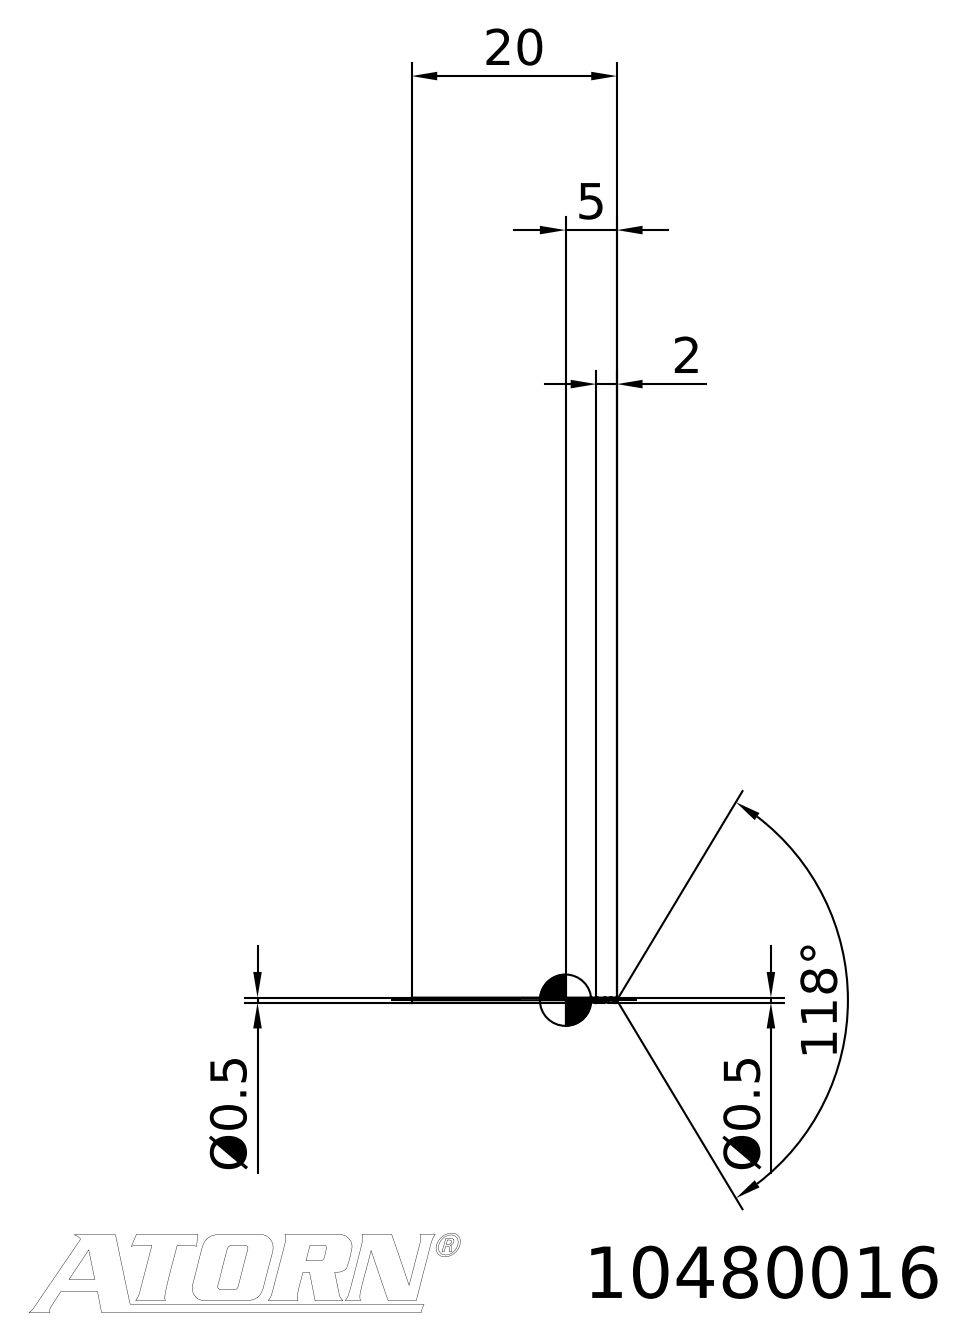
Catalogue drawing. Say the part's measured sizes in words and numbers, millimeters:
Its 3-D file was written by "TDM (AUTOMOTIVE_DESIGN)". It is 2 solids with 25 faces: 3 planar, 0 cylindrical and 22 other. Overall it measures 20 by 1.02 by 0.84 millimeters. Its volume is 4 cubic millimeters and its surface area 32 square millimeters. The main face-to-face distances are 18.
